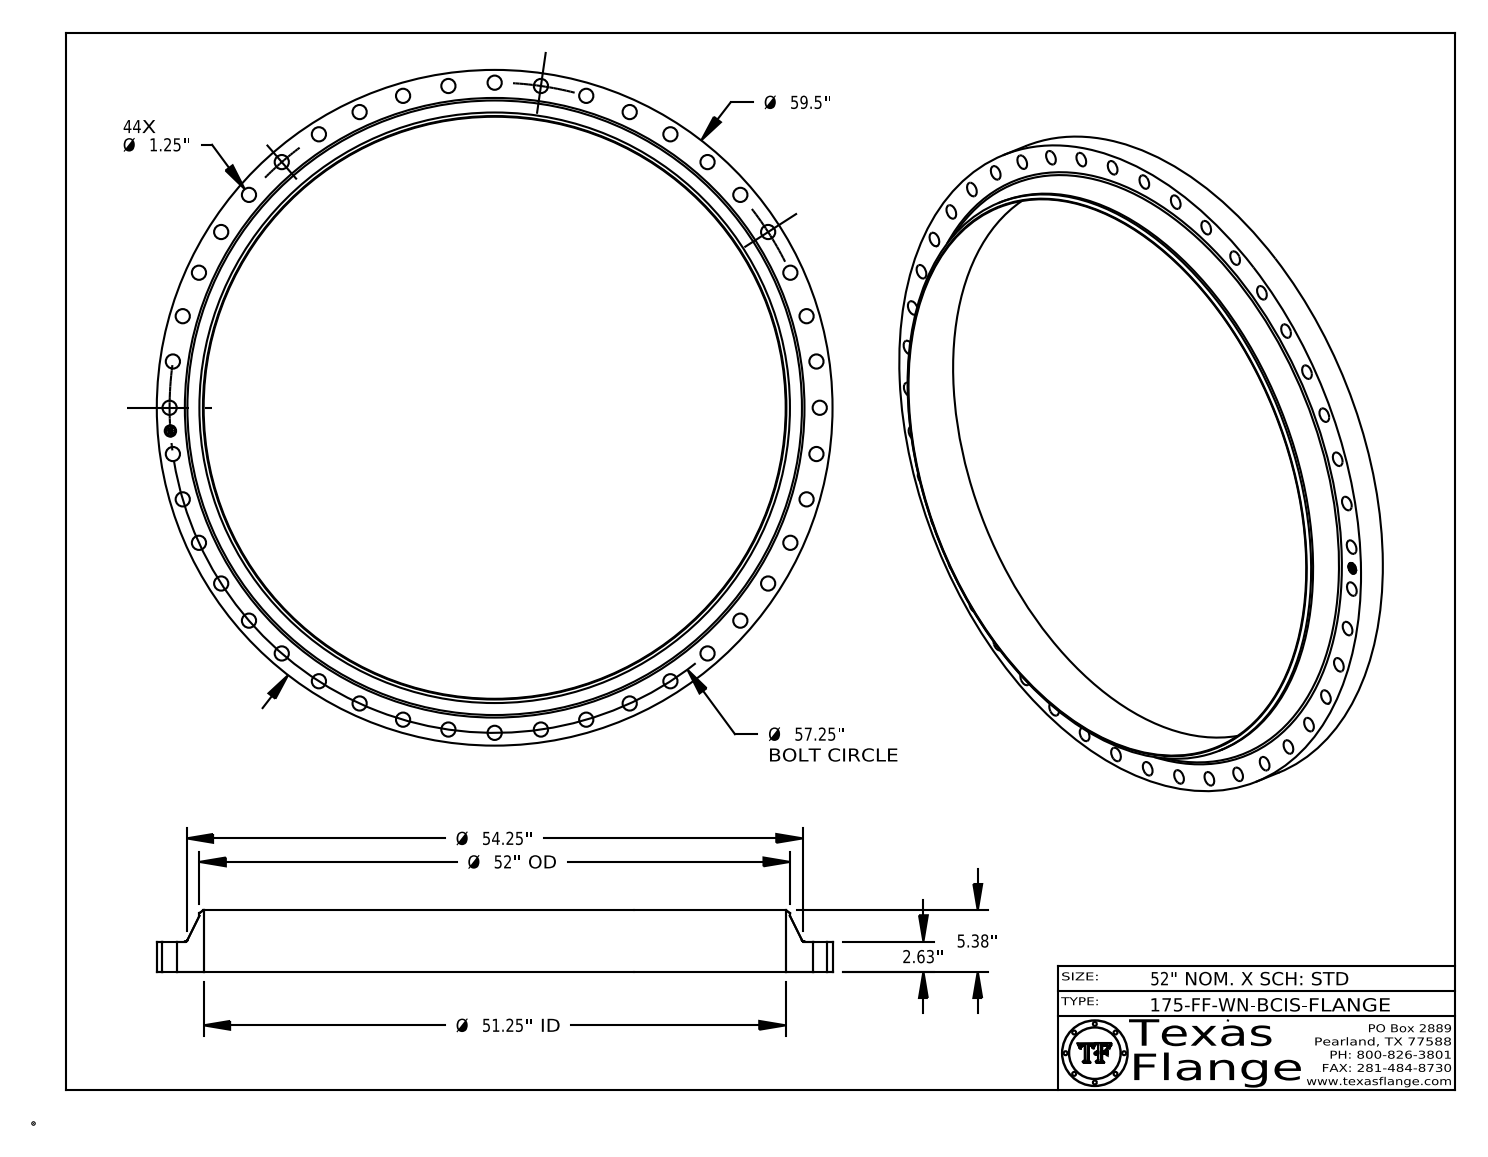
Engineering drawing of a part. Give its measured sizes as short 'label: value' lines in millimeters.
name: 175-FF-WN, BCIS
written by: CATIA V5 STEP AP214 (AUTOMOTIVE_DESIGN)
unit: mm
bodies: 1 solid, 488 faces (368 planar, 114 cylindrical, 6 other)
size: 1511.3 × 1511.3 × 136.7
volume: 34 720 000 mm³; area: 2 208 000 mm²
holes: 44× ⌀31.8, 1× ⌀25.4, 1× ⌀1301.8
bosses: 8× ⌀1.5, 1× ⌀1511.3, 1× ⌀1320.8, 1× ⌀20
face distances: 66.8, 136.7, 69.9, 66.4, 0.4, 70.2, 7.6, 7.4, 0.5, 1.4
hole spacings: 1450.4, 207, 103.7, 508.2, 727.1, 1420.9, 1099, 1322.7
